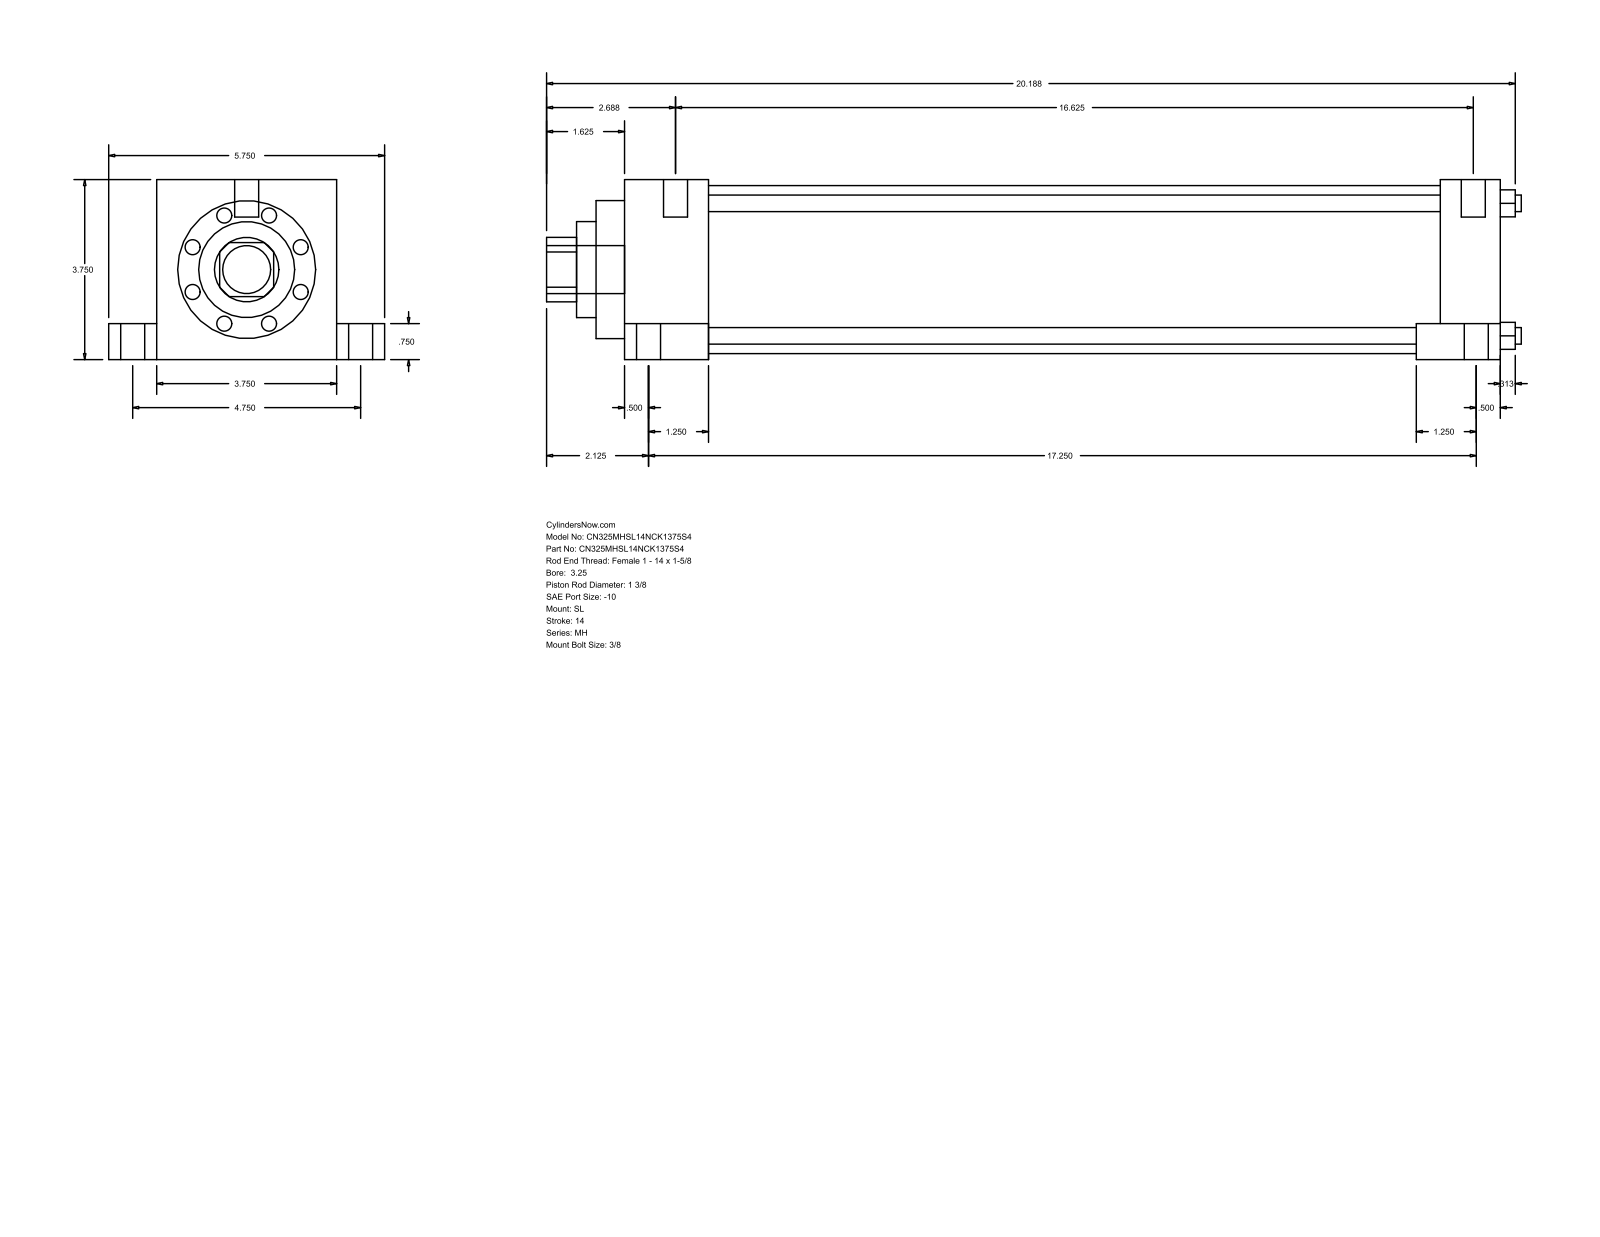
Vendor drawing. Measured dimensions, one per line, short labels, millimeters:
name: MH_SL__0325_1.375
written by: GSSL Pune (CONFIG_CONTROL_DESIGN)
unit: mm
bodies: 0 solids, 110 faces (77 planar, 33 cylindrical, 0 other)
size: 515.94 × 146.05 × 95.25
holes: 4× ⌀8.76, 1× ⌀34.92, 1× ⌀50.8, 1× ⌀73.03, 1× ⌀88.9
bosses: 6× ⌀12.7, 4× ⌀19.05, 4× ⌀5.56, 1× ⌀25.4
rounds: 1× R17.06
face distances: 95.24, 463.55, 44.45, 419.1, 25.41, 120.65, 19.05, 76.19, 431.8, 387.35
hole spacings: 49.57, 70.1, 99.14
